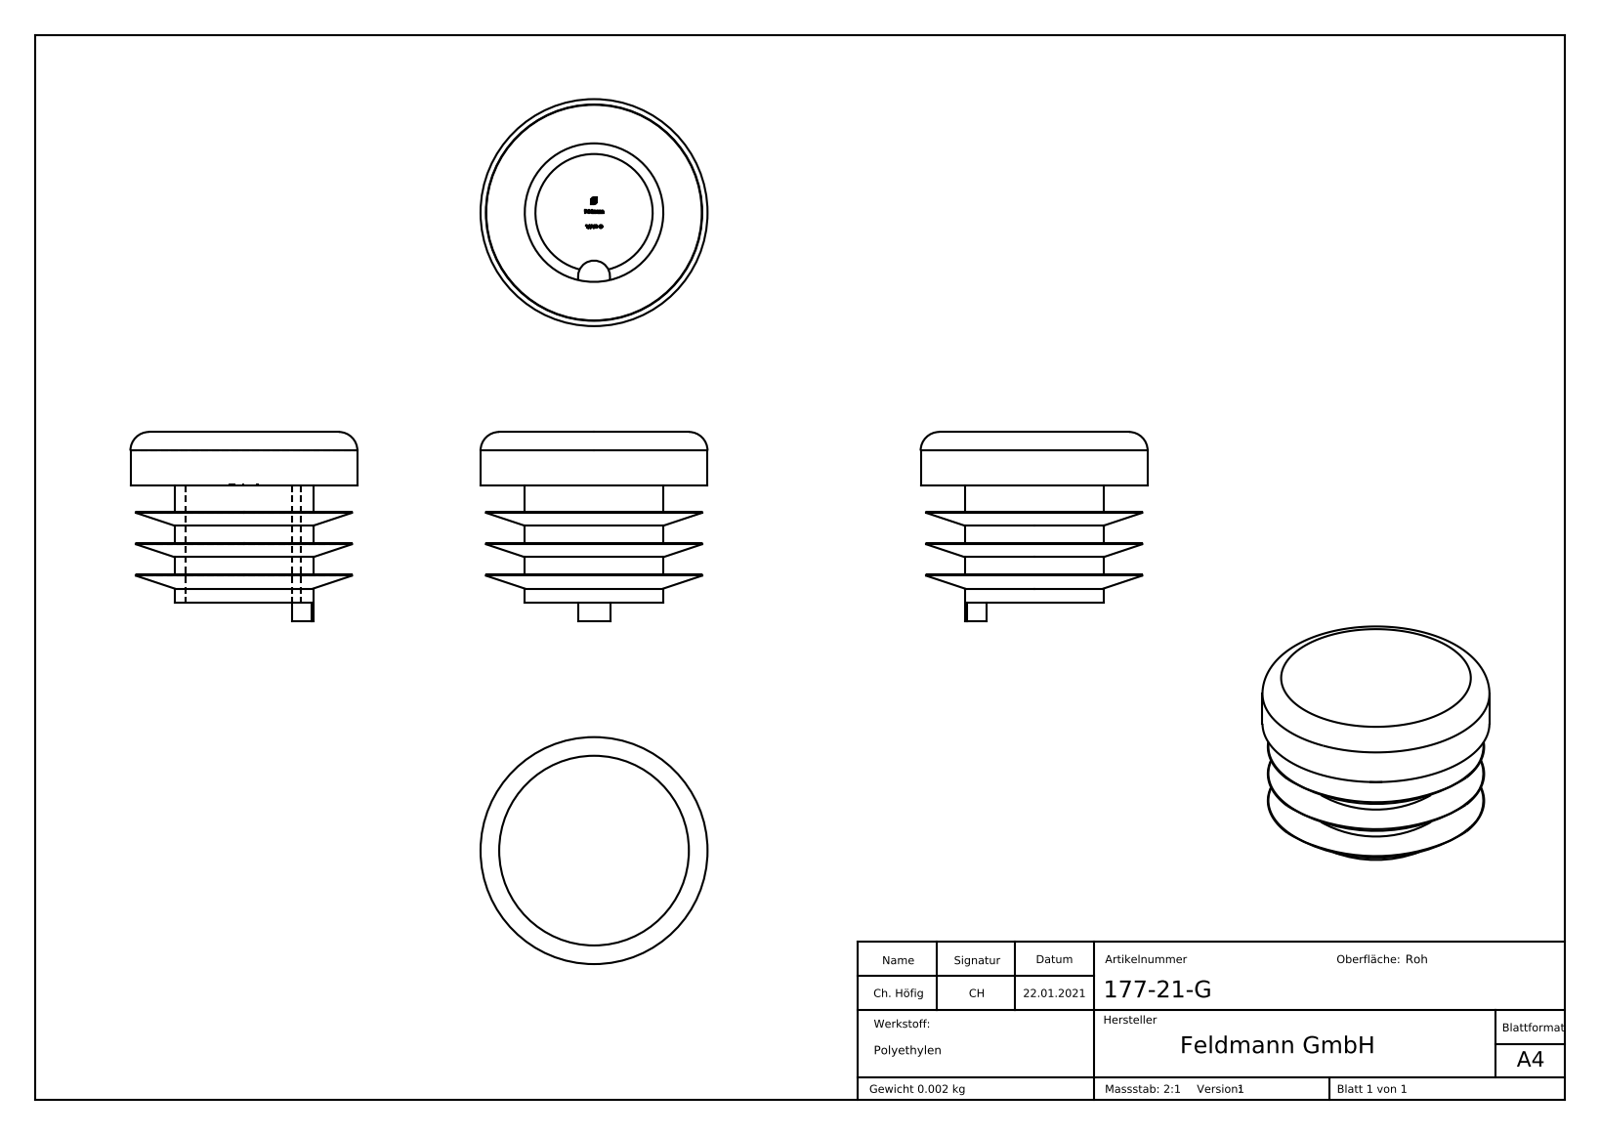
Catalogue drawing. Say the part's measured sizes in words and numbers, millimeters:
The part is named "177-21-G". Its 3-D file was written by "SolidWorks 2018 (CONFIG_CONTROL_DESIGN)". It is 1 solid with 253 faces: 144 planar, 12 cylindrical and 97 other. Overall it measures 21.3 by 21.3 by 17.8 millimeters. Its volume is 2 555 cubic millimeters and its surface area 2 877 square millimeters. Round holes: 1 of diameter 11. Round bosses or shafts: 1 of diameter 21.3, 1 of diameter 13. Partial cylindrical surfaces (rounded edges, fillets, slot ends): 1 of radius 1.5. The main face-to-face distances are 2.95, 5, 8.4, 13.4, 5.45, 10.45, 5.9, 2.5, 7.5, 2.6.
